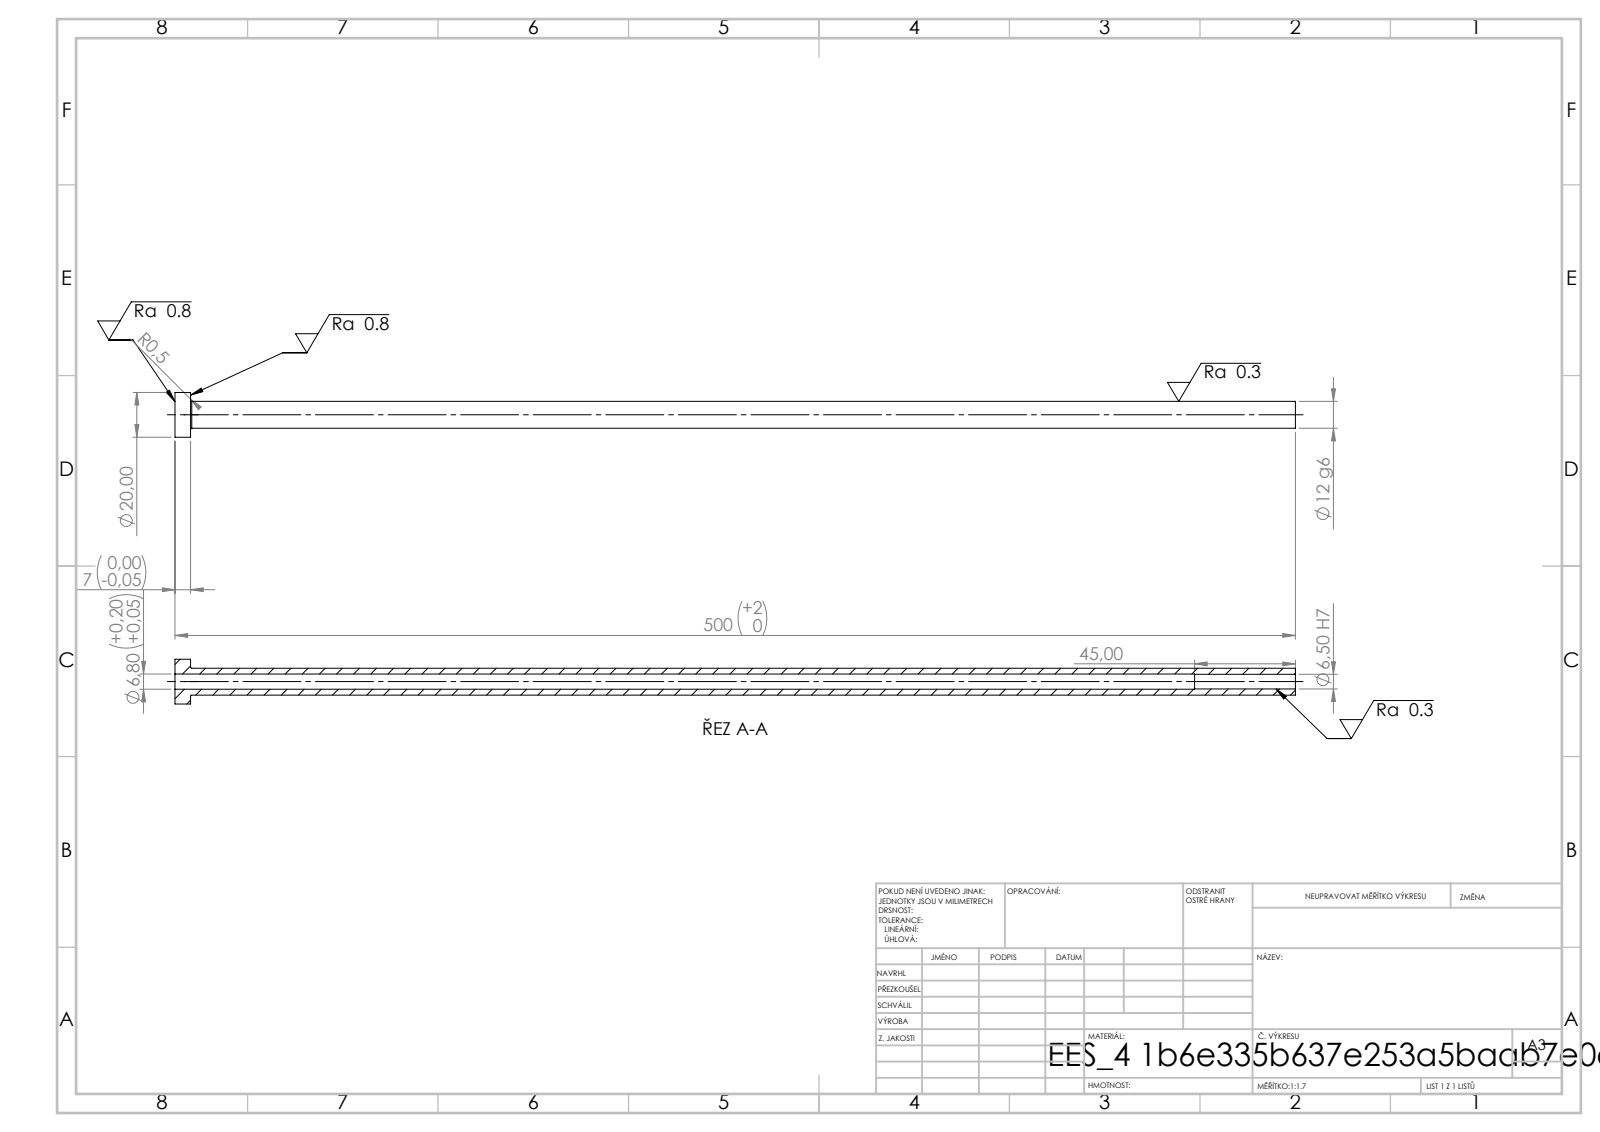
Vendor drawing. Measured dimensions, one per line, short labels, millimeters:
written by: SolidWorks 2019 (CONFIG_CONTROL_DESIGN)
unit: mm
bodies: 1 solid, 14 faces (4 planar, 8 cylindrical, 2 other)
size: 500 × 20 × 20
volume: 39 941 mm³; area: 30 218 mm²
holes: 1× ⌀6.5, 1× ⌀6.8
bosses: 1× ⌀20, 1× ⌀12
face distances: 7, 500, 493, 455, 448, 45
